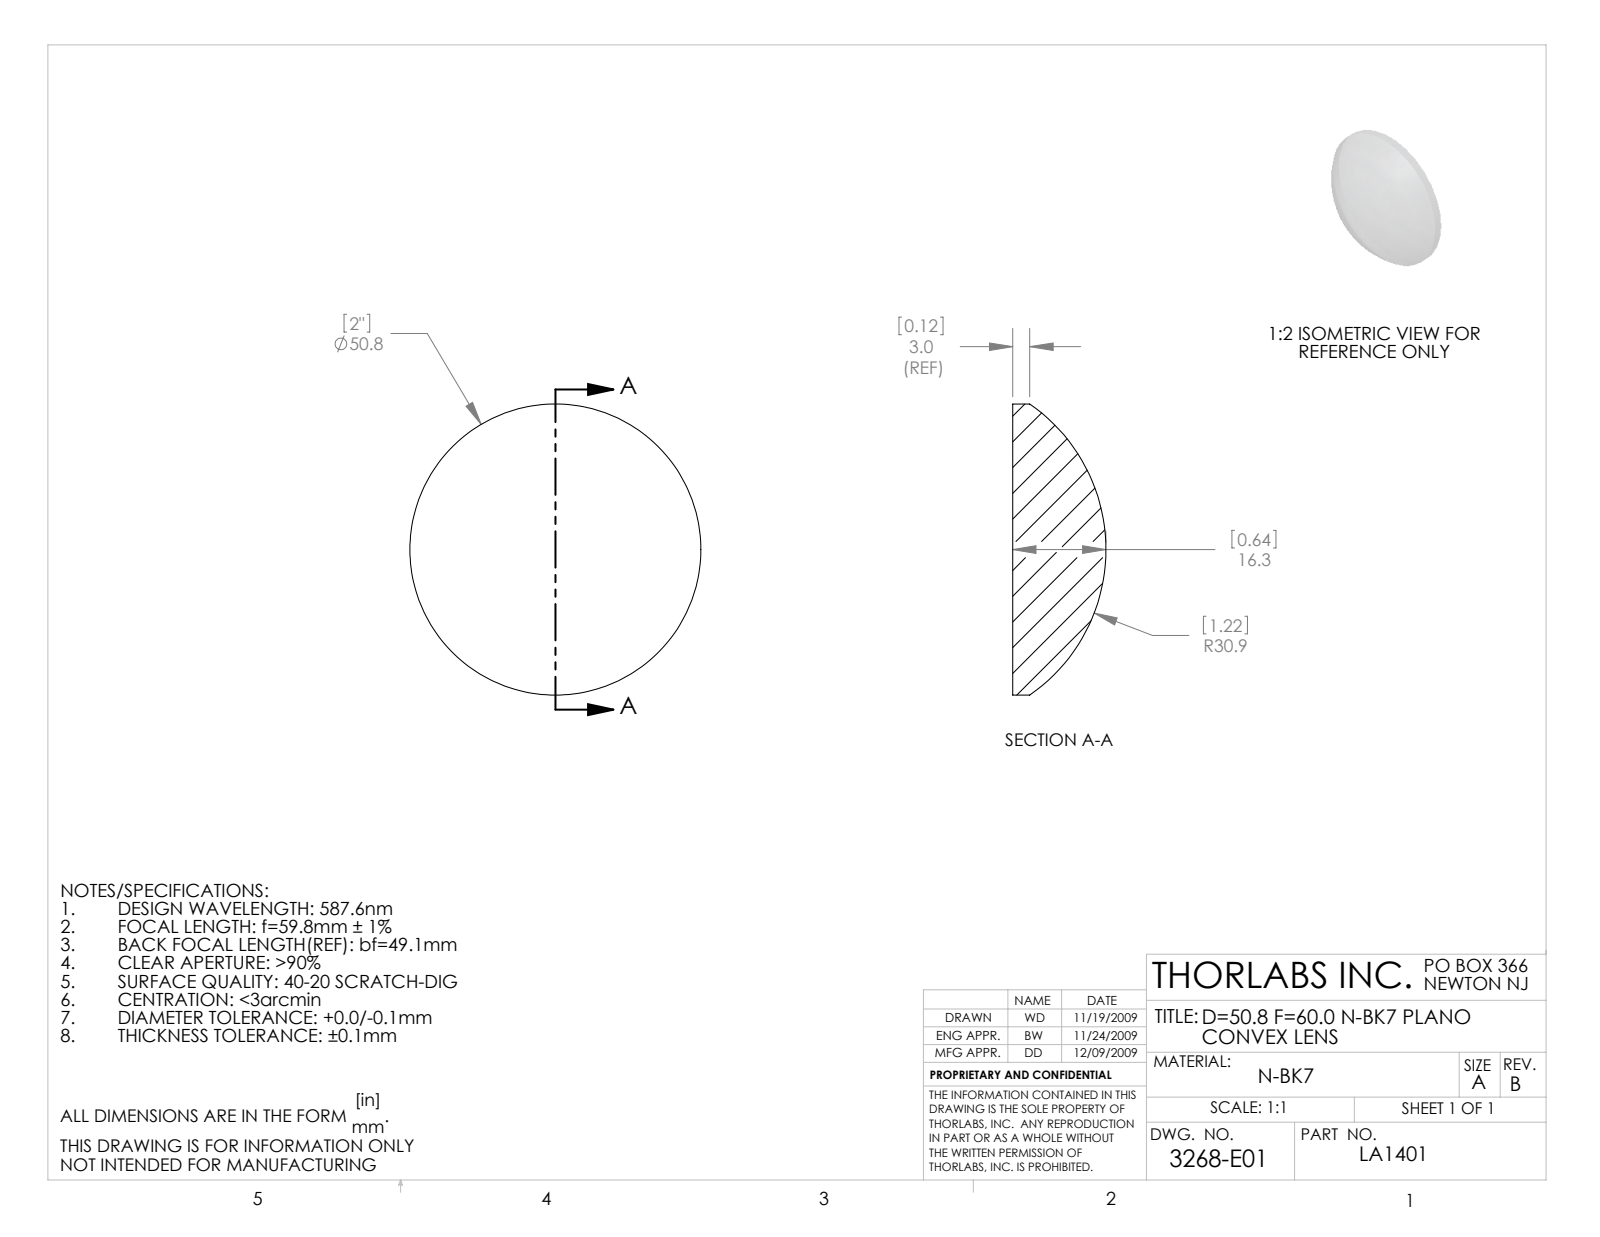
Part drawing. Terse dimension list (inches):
name: 3268-E0W
written by: SolidWorks 2009 (AUTOMOTIVE_DESIGN)
unit: in
bodies: 1 solid, 5 faces (1 planar, 2 cylindrical, 2 other)
size: 2 × 2 × 0.641
volume: 1.267 in³; area: 7.883 in²
bosses: 1× ⌀2
